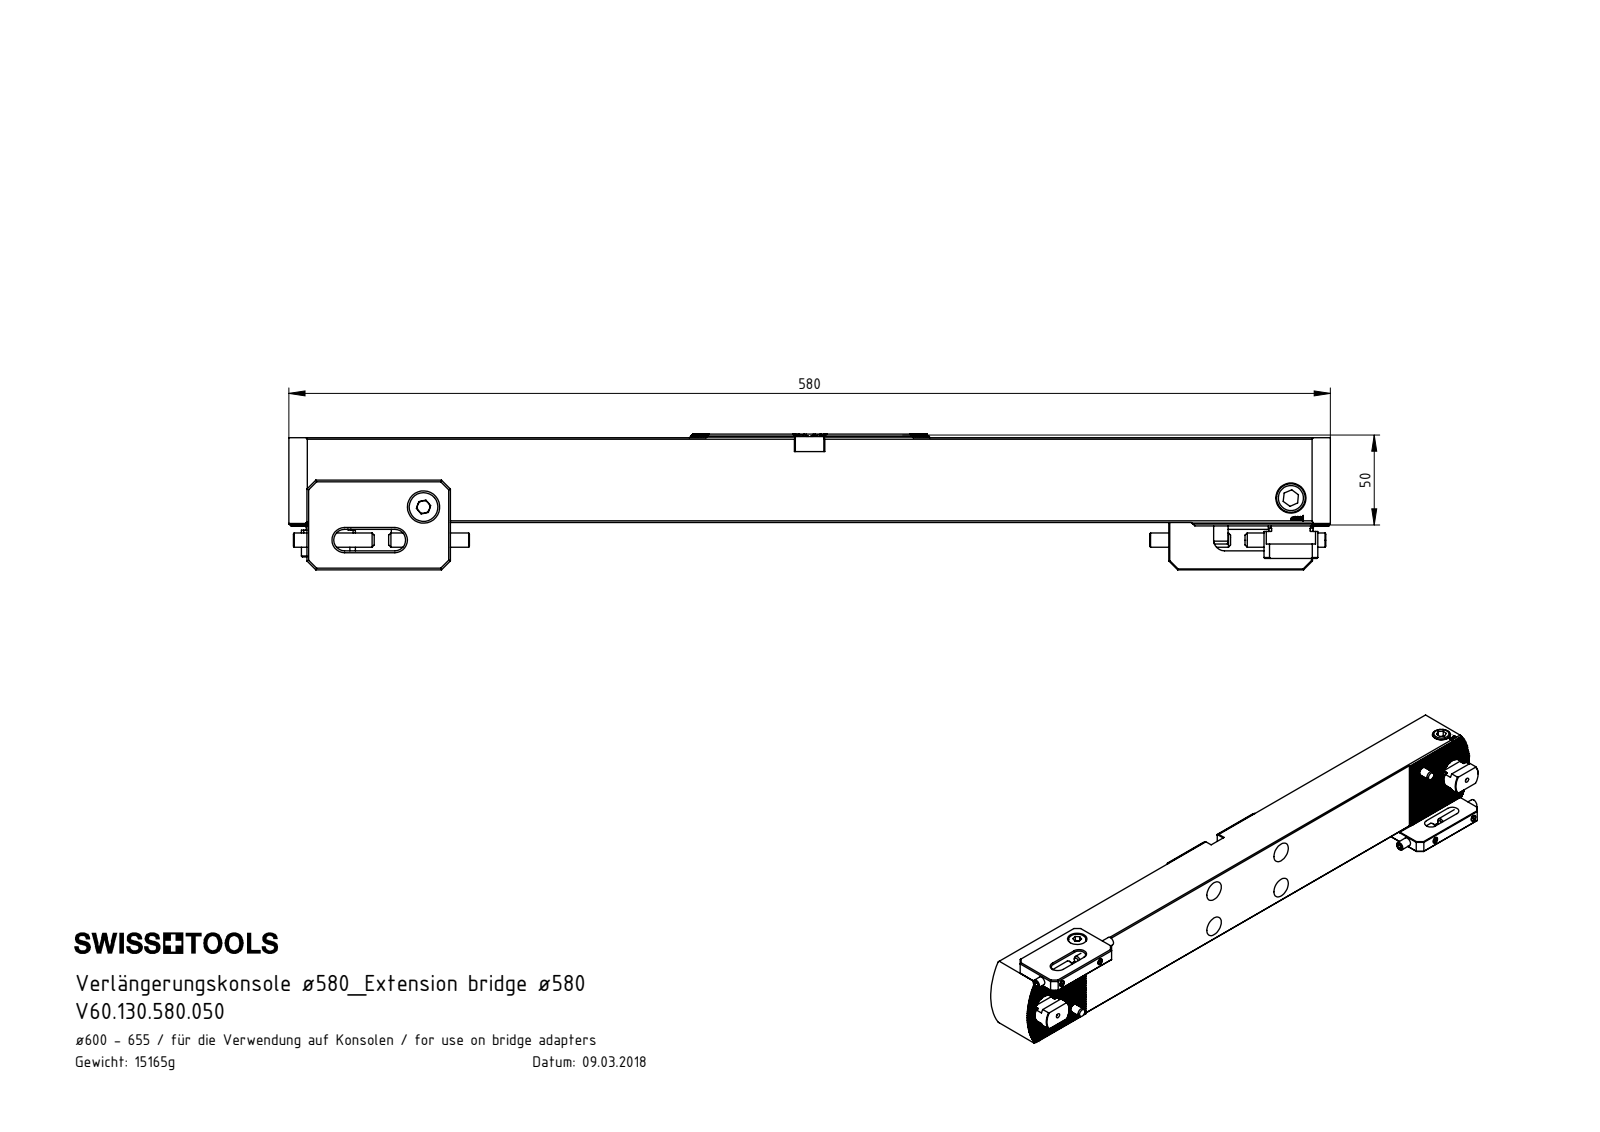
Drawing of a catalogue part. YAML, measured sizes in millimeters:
part_name: "DIN 7984 - M10 x 16; Ko1-VK1.580.050_E; VK1-ER7.001.012_mit langer Schraube; VK1-ER2.001.044_A (+8 more)"
step_written_by: "SolidWorks 2017 (AUTOMOTIVE_DESIGN)"
units: millimeters
bodies: {solids: 27, faces: 1319, planar: 854, cylindrical: 260, other: 205}
overall_size: [580, 94, 75.58]
volume: 1938000
surface_area: 225847
round_holes:
  - {diameter: 5, count: 4}
  - {diameter: 6, count: 4}
  - {diameter: 6.8, count: 4}
  - {diameter: 13, count: 4}
  - {diameter: 19, count: 4}
  - {diameter: 2, count: 2}
  - {diameter: 8, count: 2}
  - {diameter: 8.5, count: 2}
  - {diameter: 10.5, count: 2}
  - {diameter: 11, count: 2}
  - {diameter: 14, count: 2}
  - {diameter: 18, count: 2}
round_bosses_or_shafts:
  - {diameter: 16, count: 4}
  - {diameter: 6, count: 4}
  - {diameter: 10, count: 2}
  - {diameter: 8, count: 2}
partial_cylinders:
  - {radius: 0.14, count: 66}
  - {radius: 2, count: 8}
  - {radius: 6, count: 4}
  - {radius: 12.3, count: 2}
  - {radius: 15, count: 2}
  - {radius: 65, count: 2}
  - {radius: 7.95, count: 1}
face_to_face_distances: [47.16, 70, 12, 82, 1.73, 8.66, 3.46, 6.93, 0.5, 41.57]
hole_center_spacings: [536, 224.89, 312.64, 7.9, 18.55, 19.61, 34.53, 35.09]
